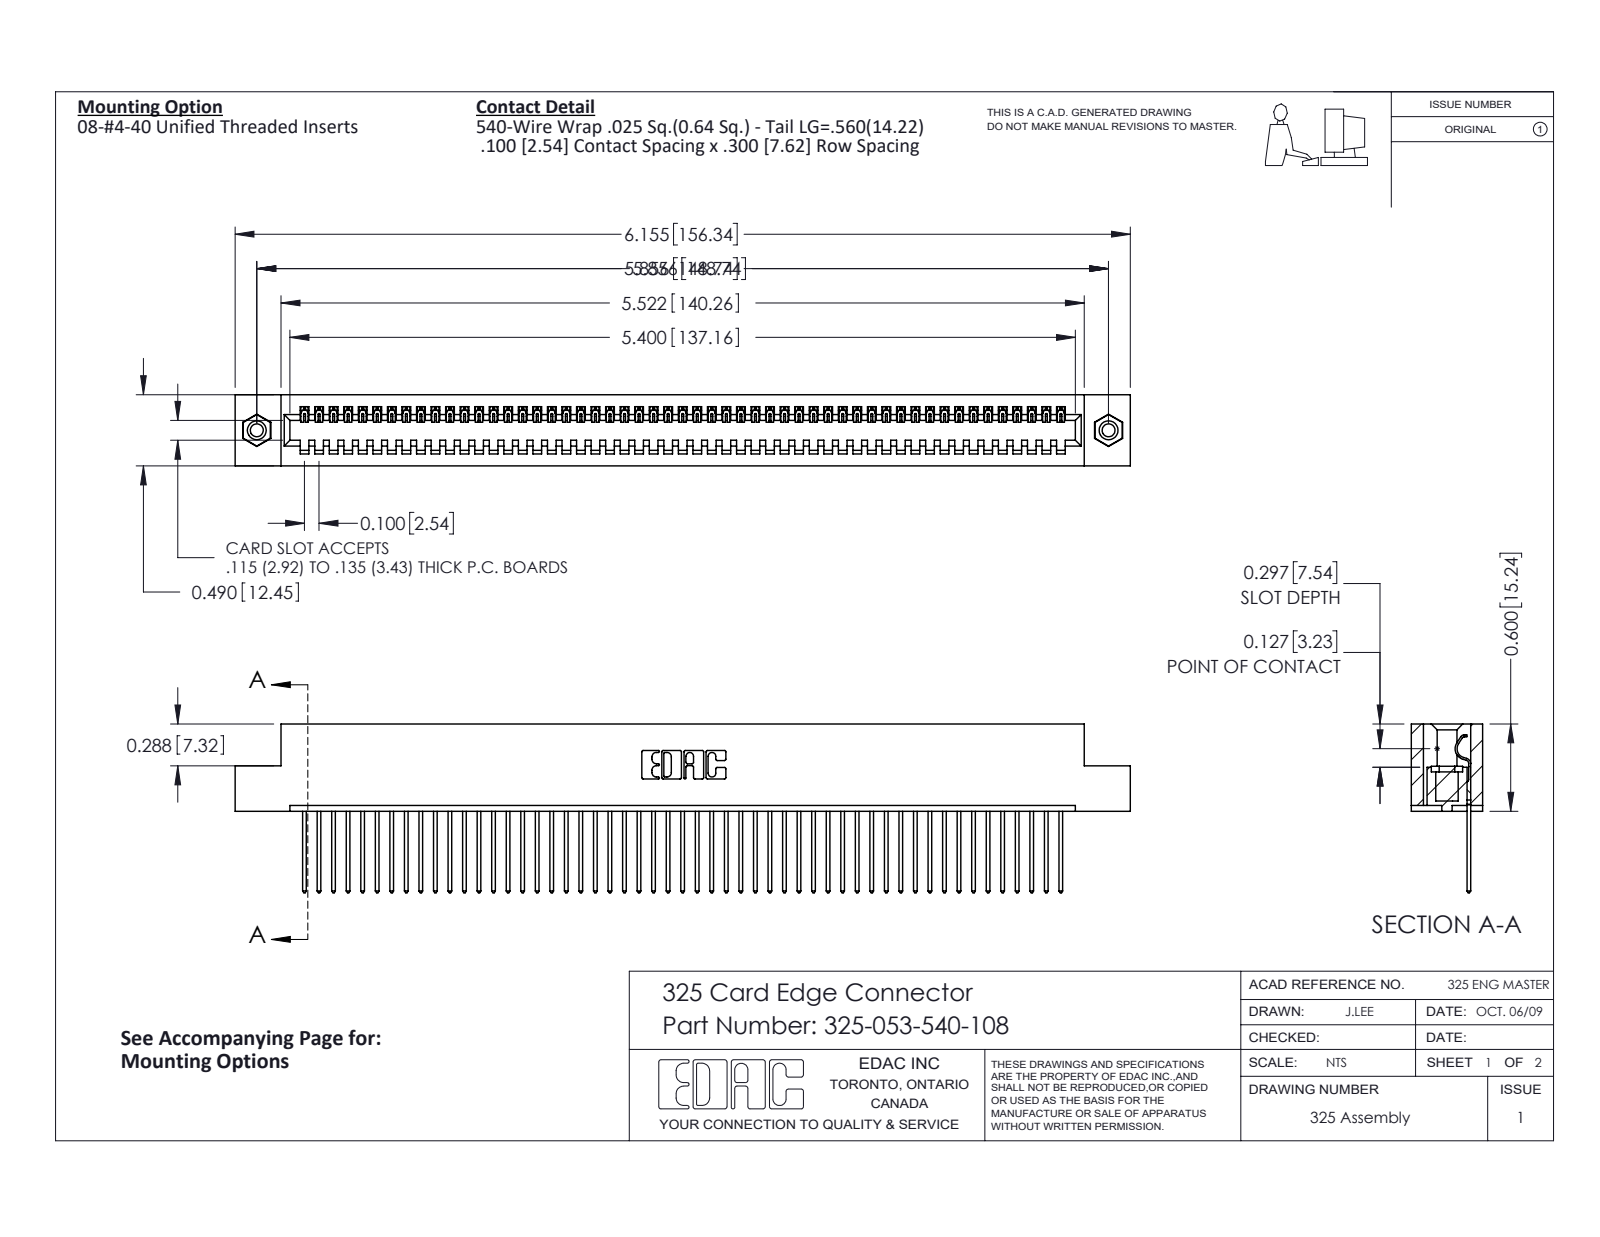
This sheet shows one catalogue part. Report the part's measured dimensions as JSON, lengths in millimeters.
{"part_name": "325-292-001_325-293-140; 345-250-001_345-250-003-102; 325 Part_TI; 325-053-540-108", "step_written_by": "SolidWorks 2016 (CONFIG_CONTROL_DESIGN)", "units": "millimeters", "bodies": {"solids": 56, "faces": 3248, "planar": 2328, "cylindrical": 904, "other": 16}, "overall_size": [156.3, 29.5, 12.4], "volume_mm3": 19990, "surface_area_mm2": 22580, "round_holes": [[2.3, 2], [3.2, 2], [4.1, 2]], "round_bosses_or_shafts": [[3.9, 2]], "partial_cylinders_radius": [[0.2, 106], [0.3, 106], [0.3, 22], [0.2, 6], [0.8, 6], [0.7, 3], [0.4, 1], [0.6, 1]], "face_to_face_distances": [2.1, 10.3, 12.4, 7.6, 2.7, 9.7, 0.6, 8.3, 14.2, 6.7], "hole_center_spacings": [148.7]}
